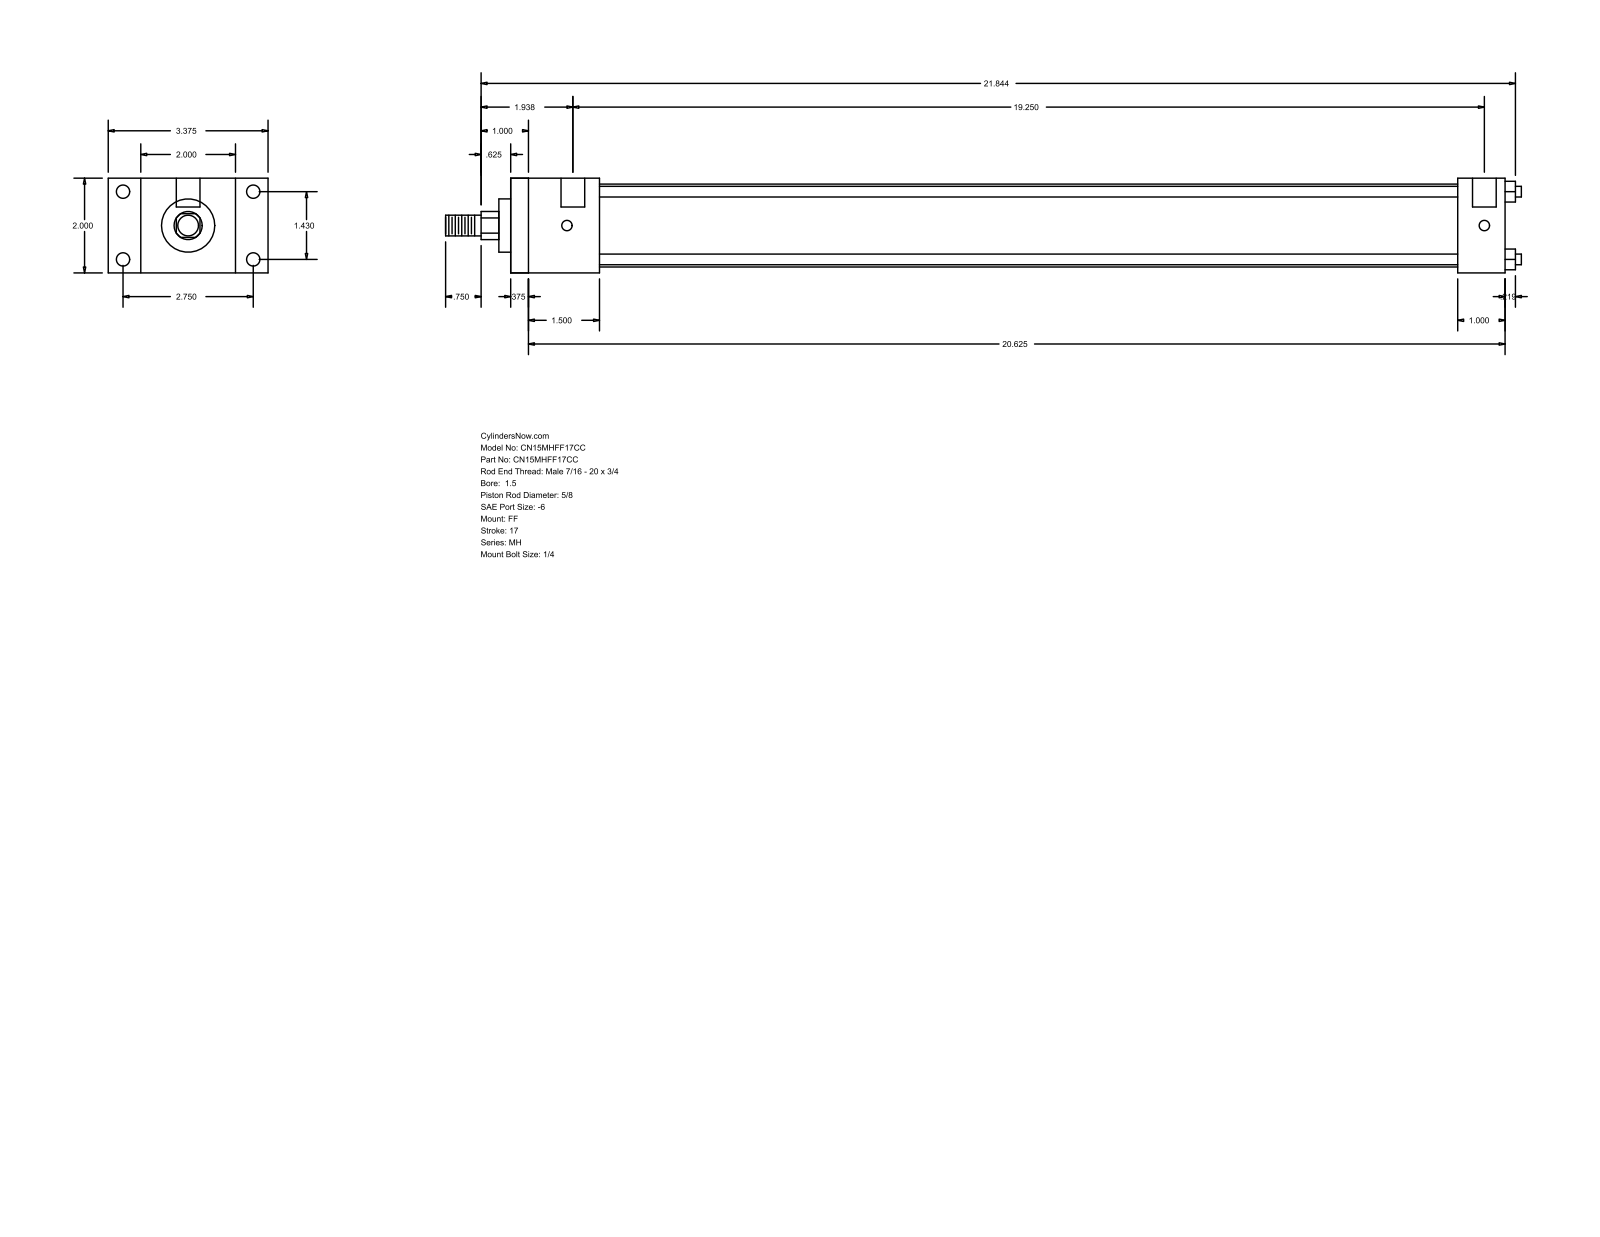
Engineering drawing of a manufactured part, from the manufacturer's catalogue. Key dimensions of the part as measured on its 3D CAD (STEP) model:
Part name (STEP PRODUCT): MH_FF__0150_0.625
STEP written by: GSSL Pune (CONFIG_CONTROL_DESIGN)
Units: millimetres
Bodies: 0 solids, 92 faces (64 planar, 28 cylindrical, 0 other)
Overall size (bounding box): 577.06 × 85.72 × 50.8
Round holes (diameter × count): ⌀5.56 ×4, ⌀7.14 ×4, ⌀12.7 ×2
Round bosses / shafts (diameter × count): ⌀5.71 ×4, ⌀44.45 ×1, ⌀28.57 ×1, ⌀15.88 ×1, ⌀11.11 ×1
Partial cylindrical surfaces — rounded edges, fillets, slot ends (radius × count): R7.54 ×1
Main face-to-face distances: 50.8, 533.39, 9.52, 523.87, 17.46, 68.26, 47.62, 38.1, 485.77, 508
Hole centre spacings: 36.32, 69.84, 78.72, 492.12, 3.17, 488.95
